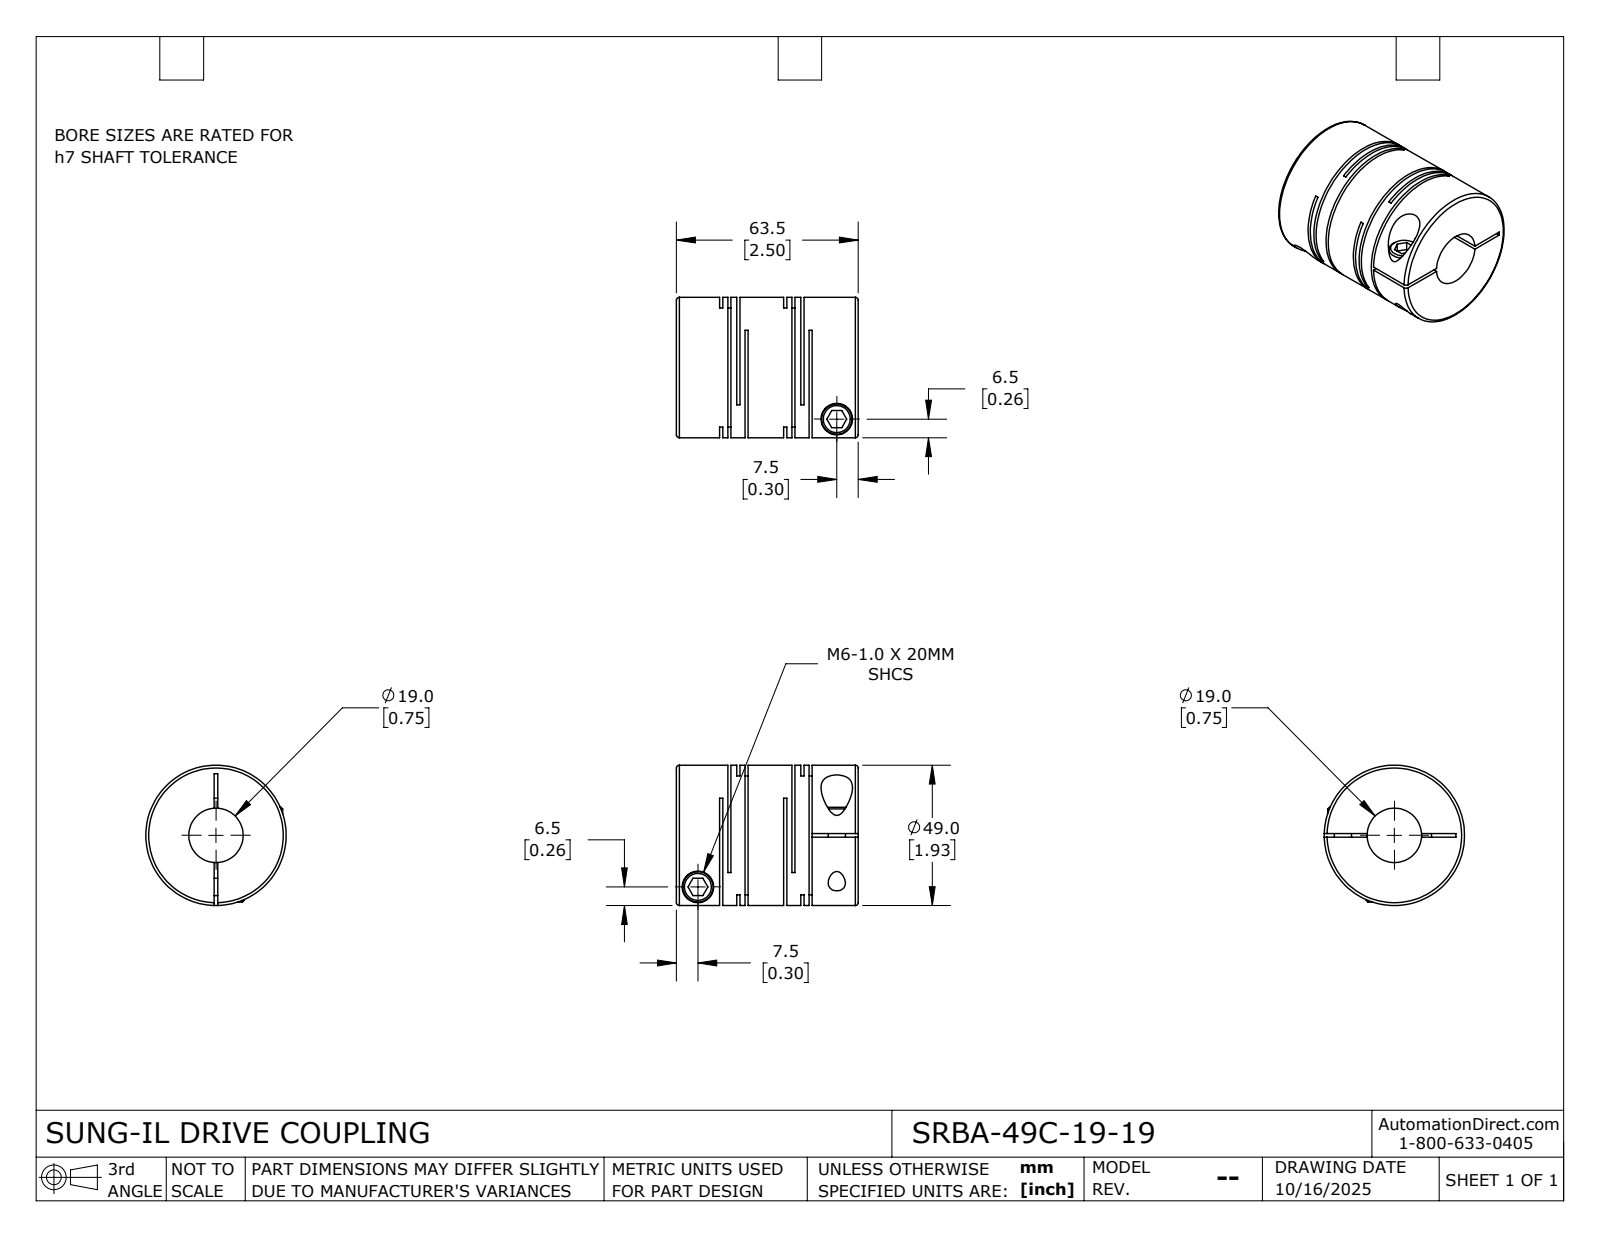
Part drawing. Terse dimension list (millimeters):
name: SRBA-49C-19-19
written by: SolidWorks 2024 (CONFIG_CONTROL_DESIGN)
unit: mm
bodies: 1 solid, 115 faces (60 planar, 42 cylindrical, 13 other)
size: 63.5 × 49 × 49
volume: 87 844 mm³; area: 38 412 mm²
holes: 2× ⌀6, 2× ⌀11, 1× ⌀19
bosses: 2× ⌀10.6, 1× ⌀49
face distances: 6, 1.1, 22.35, 2.85, 21.25, 3.15, 1.75, 4.9, 19.5, 16.35
